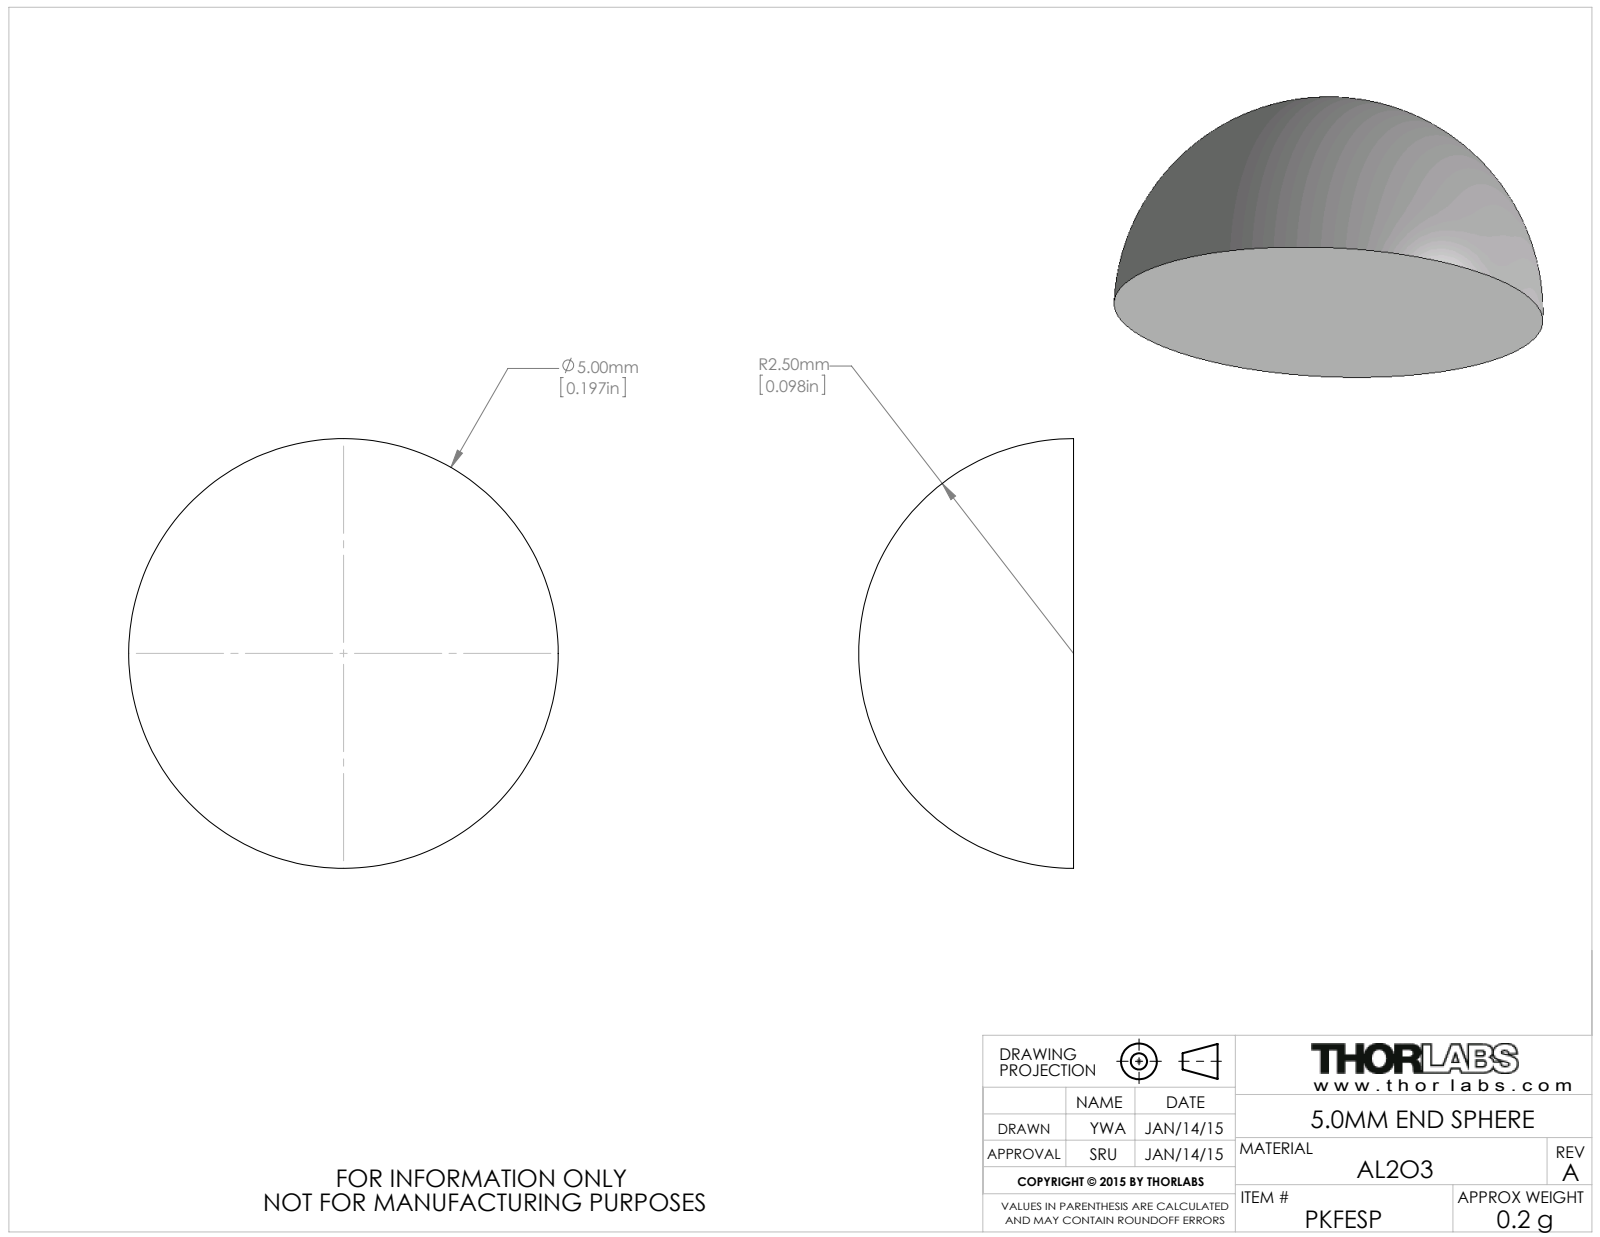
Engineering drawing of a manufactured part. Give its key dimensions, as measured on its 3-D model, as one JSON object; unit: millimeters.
{"part_name": "PKFESP", "step_written_by": "SolidWorks 2012 (AUTOMOTIVE_DESIGN)", "units": "millimeters", "bodies": {"solids": 1, "faces": 3, "planar": 1, "cylindrical": 0, "other": 2}, "overall_size": [5, 5, 2.5], "volume_mm3": 33, "surface_area_mm2": 59}
